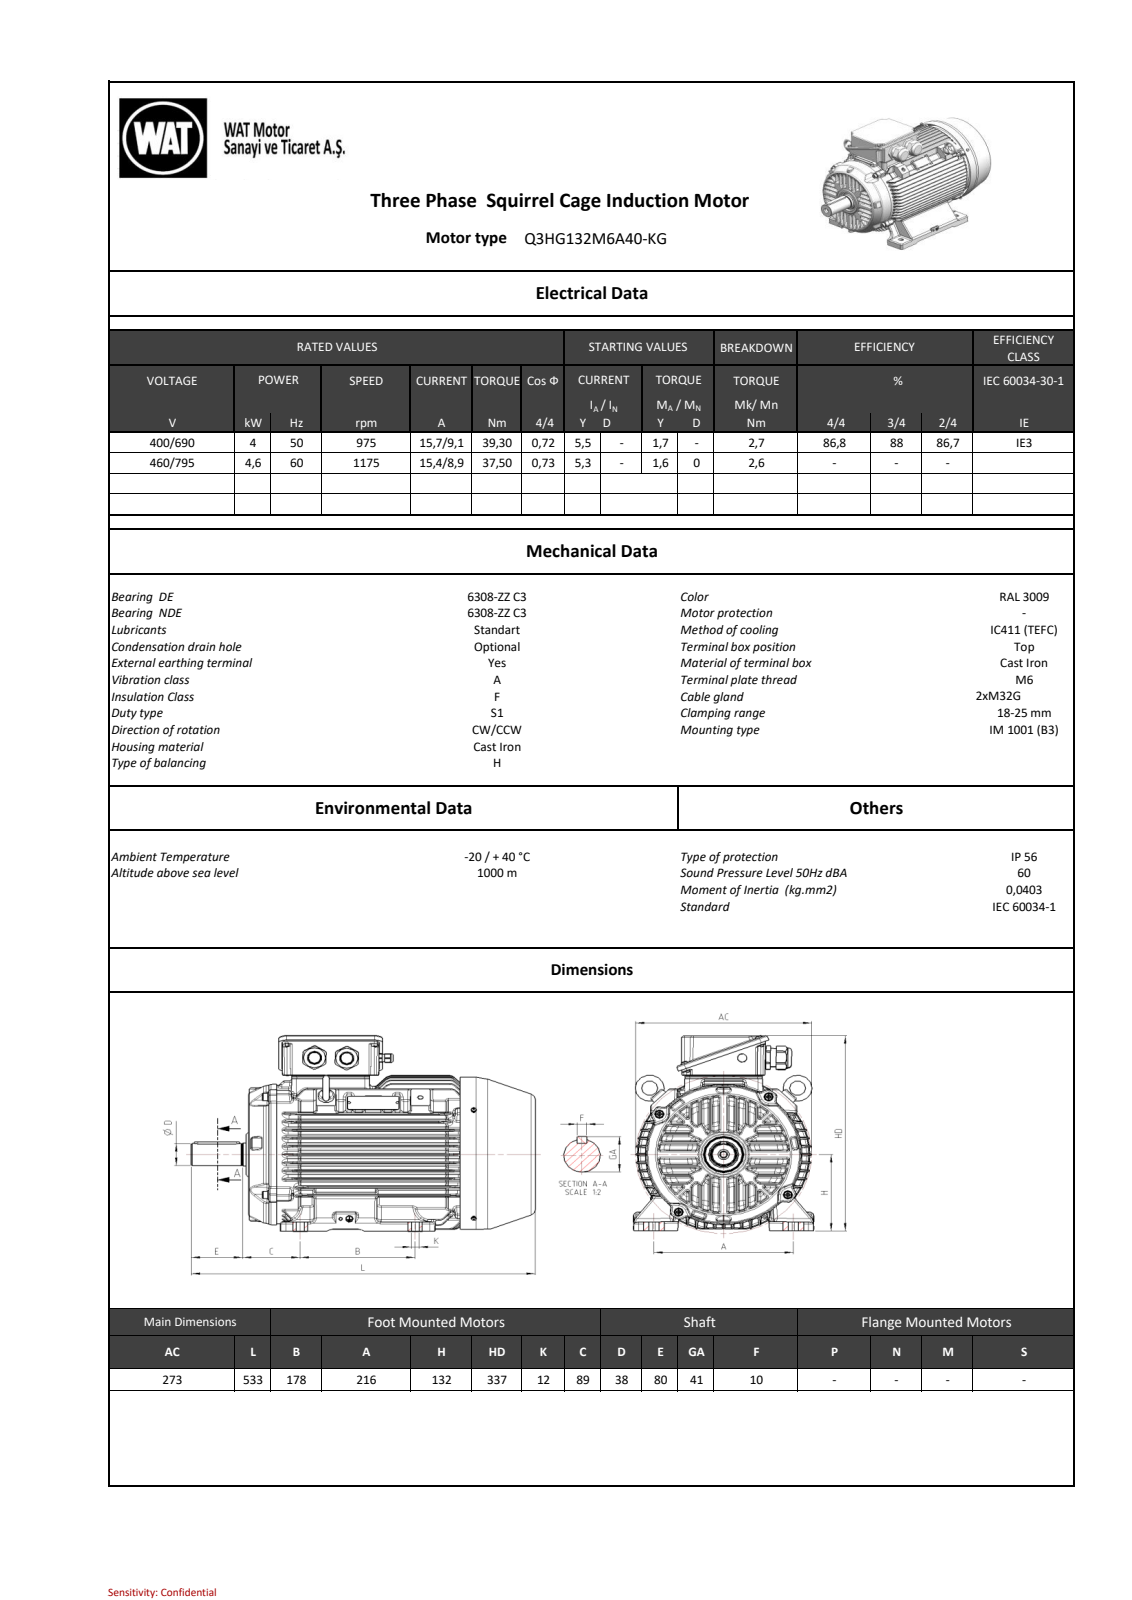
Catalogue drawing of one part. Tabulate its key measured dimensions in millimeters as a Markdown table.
| quantity | value |
| --- | --- |
| part name | 260021E4F5C7p82x |
| STEP written by | SIEMENS PLM Software NX 11.0 (AUTOMOTIVE_DESIGN) |
| units | millimeters |
| bodies | 0 solids, 6665 faces (1198 planar, 1826 cylindrical, 3641 other) |
| overall size | 533 × 337.41 × 279.6 |
| round holes (diameter × count) | 5.5 × 8, 6.8 × 8, 4.2 × 3, 2.5 × 2, 8.5 × 2, 19 × 2, 21 × 2, 5 × 1, 10.3 × 1, 13 × 1, 34.2 × 1, 58.4 × 1 |
| round bosses / shafts (diameter × count) | 13 × 4, 8.65 × 4, 8 × 4, 36 × 2, 34.5 × 2, 31.25 × 2, 25 × 2, 14.8 × 2 |
| partial cylindrical surfaces (radius × count) | 4 × 299, 3 × 162, 2 × 119, 1.5 × 106, 1.8 × 64, 6 × 32, 1 × 24, 5 × 24 |
| main face-to-face distances | 55.94, 13.76, 13.83, 27.59, 110.18, 82.59, 96.35, 27.73, 41.49, 13.9 |
| hole center spacings | 136, 121.5, 171.83, 123.22, 183.51, 183.52, 123.21, 42.2 |
